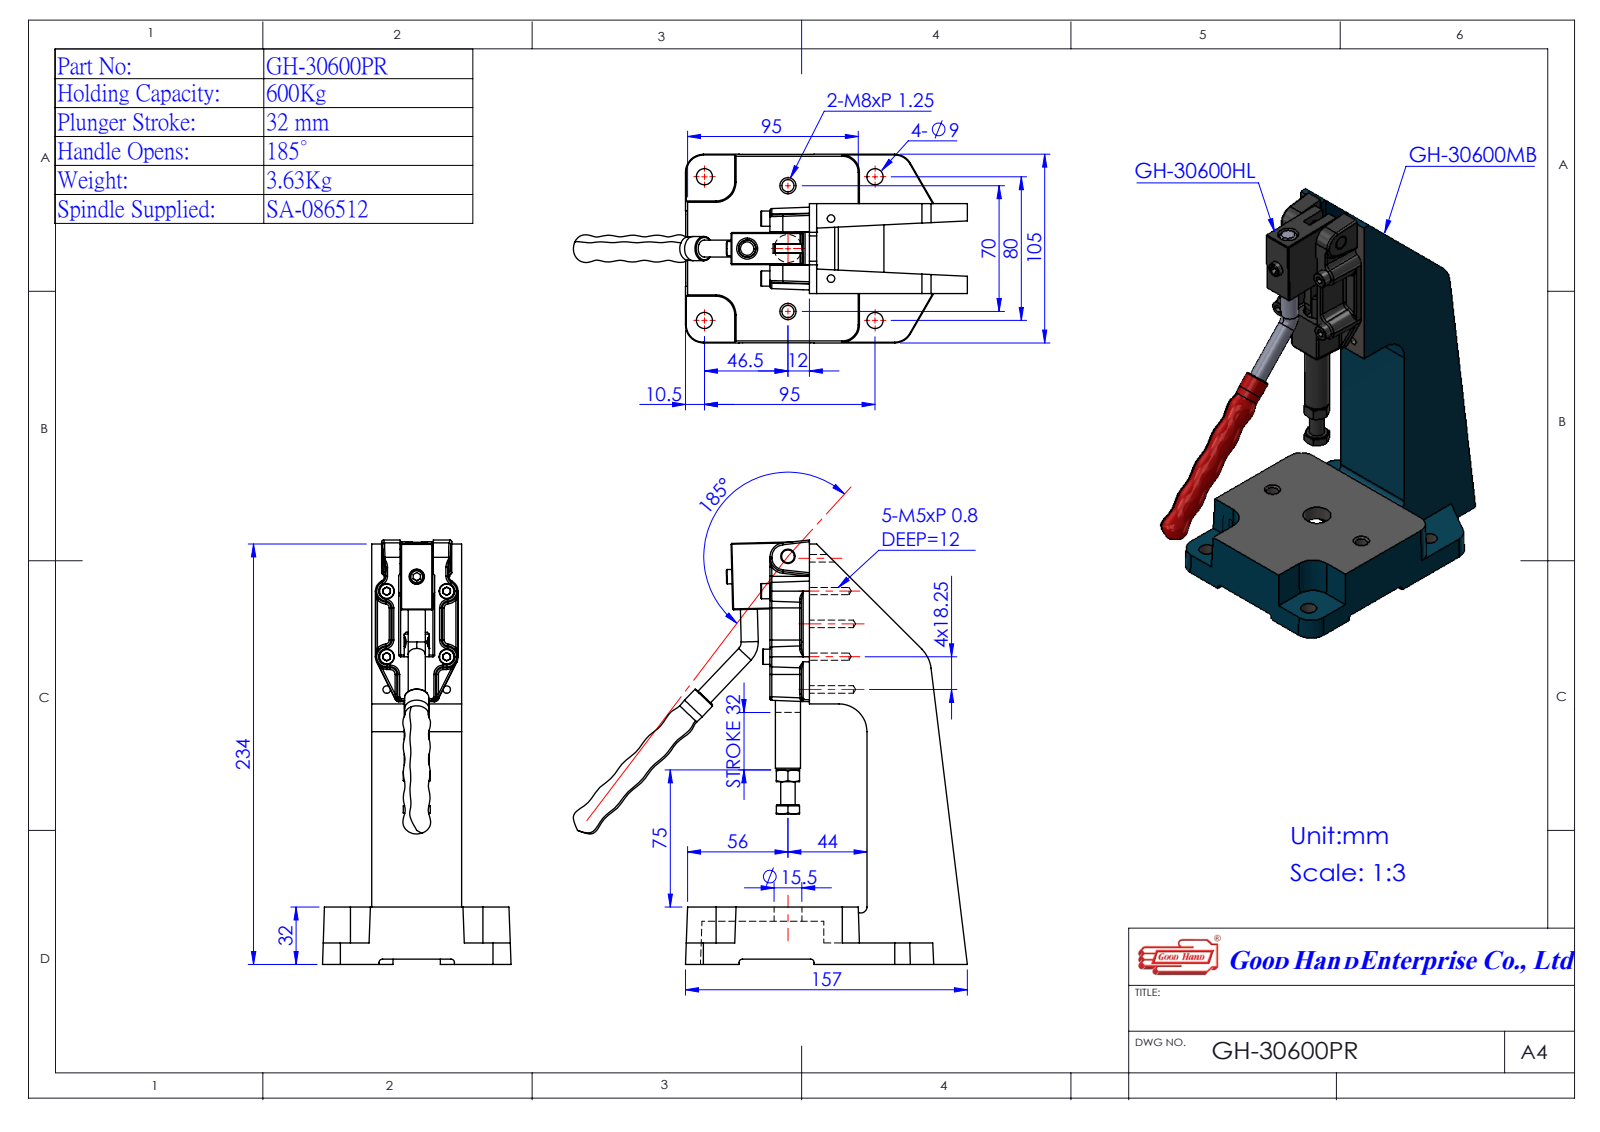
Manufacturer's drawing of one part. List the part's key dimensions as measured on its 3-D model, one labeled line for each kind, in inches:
Part name (STEP PRODUCT): Group5^GH-30600PR(簡化)-2; Group4^GH-30600PR(簡化)-2; GH-30600PR(簡化)-2; GH-30600MB(簡化)-1^GH-30600PR(簡化)-2 (+3 more)
STEP written by: SolidWorks 2016 (AUTOMOTIVE_DESIGN)
Units: inches
Bodies: 6 solids, 607 faces (171 planar, 180 cylindrical, 256 other)
Overall size (bounding box): 9.301 × 8.581 × 4.134
Volume: 34.41 in³ · Surface area: 227.5 in²
Round holes (diameter × count): ⌀0.165 ×10, ⌀0.354 ×4, ⌀0.177 ×2, ⌀0.268 ×2, ⌀0.236 ×1, ⌀0.266 ×1, ⌀0.547 ×1, ⌀0.61 ×1
Round bosses / shafts (diameter × count): ⌀0.335 ×4, ⌀0.197 ×4, ⌀0.374 ×2, ⌀0.531 ×1, ⌀0.512 ×1, ⌀0.315 ×1, ⌀0.177 ×1
Partial cylindrical surfaces — rounded edges, fillets, slot ends (radius × count): R0.079 ×7, R0.039 ×4, R0.295 ×2, R0.131 ×1, R0.315 ×1, R0.394 ×1, R0.61 ×1, R0.709 ×1
Main face-to-face distances: 1.969, 1.26, 0.945, 0.315, 0.47, 0.475, 0.79, 0.374, 1.634, 0.634
Hole centre spacings: 0.719, 1.495, 1.437, 1.945, 1.311, 2.156, 2.523, 1.378
